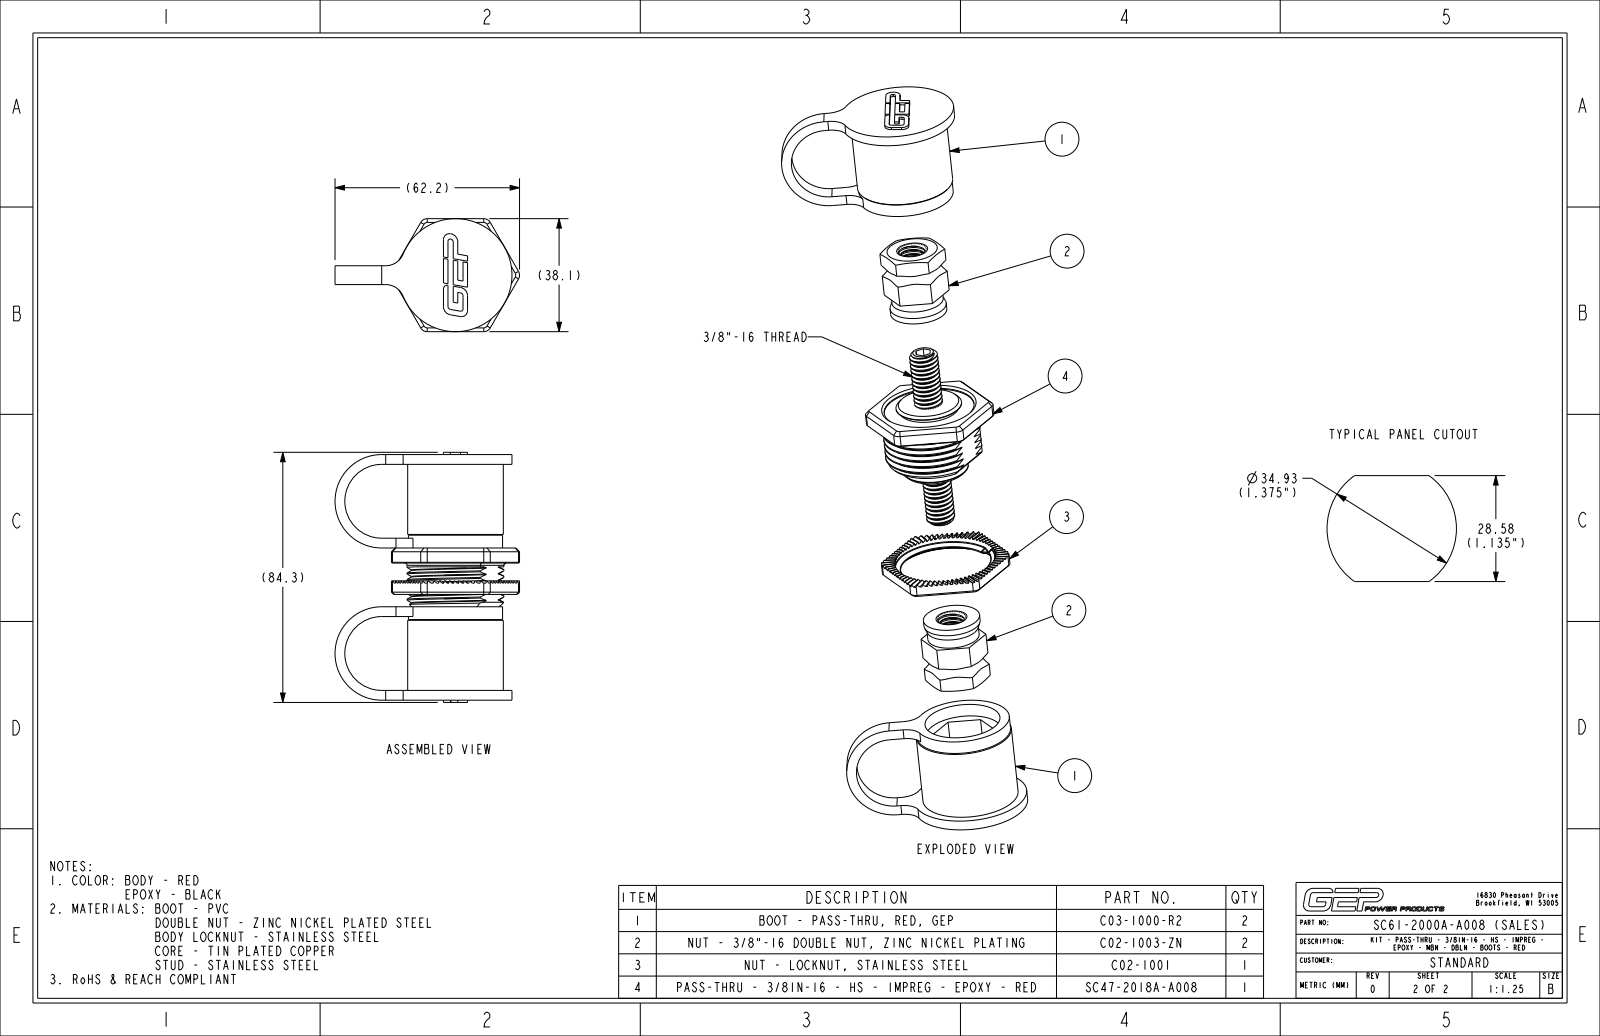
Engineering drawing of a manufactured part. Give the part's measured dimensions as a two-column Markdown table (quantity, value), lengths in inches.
| quantity | value |
| --- | --- |
| part name | C07-1001_NCF; PC40-2004A-B008_MOLD_NCF; PC40-2004A-B008_NCF_ASM; PC05-2015A-A000_NCF (+8 more) |
| STEP written by | CREO PARAMETRIC BY PTC INC, 2024014 (CONFIG_CONTROL_DESIGN) |
| units | inches |
| bodies | 10 solids, 1285 faces (746 planar, 279 cylindrical, 260 other) |
| overall size | 3.32 × 2.198 × 1.759 |
| volume | 4.232 in³ |
| surface area | 63.54 in² |
| round holes (diameter × count) | 0.313 × 1, 0.715 × 1, 0.875 × 1, 1 × 1, 1.2 × 1, 1.347 × 1 |
| round bosses / shafts (diameter × count) | 1.5 × 1, 1.27 × 1, 1.25 × 1, 0.875 × 1, 0.75 × 1, 0.715 × 1, 0.685 × 1, 0.375 × 1 |
| partial cylindrical surfaces (radius × count) | 0.03 × 6, 0.04 × 6, 0.1 × 6, 0.11 × 6, 0.08 × 4, 0.25 × 4, 0.05 × 2, 0.49 × 2 |
| main face-to-face distances | 0.75, 0.17, 1.24, 2.02, 0.13, 3.26, 1.07, 2.19, 0.25, 0.83 |
